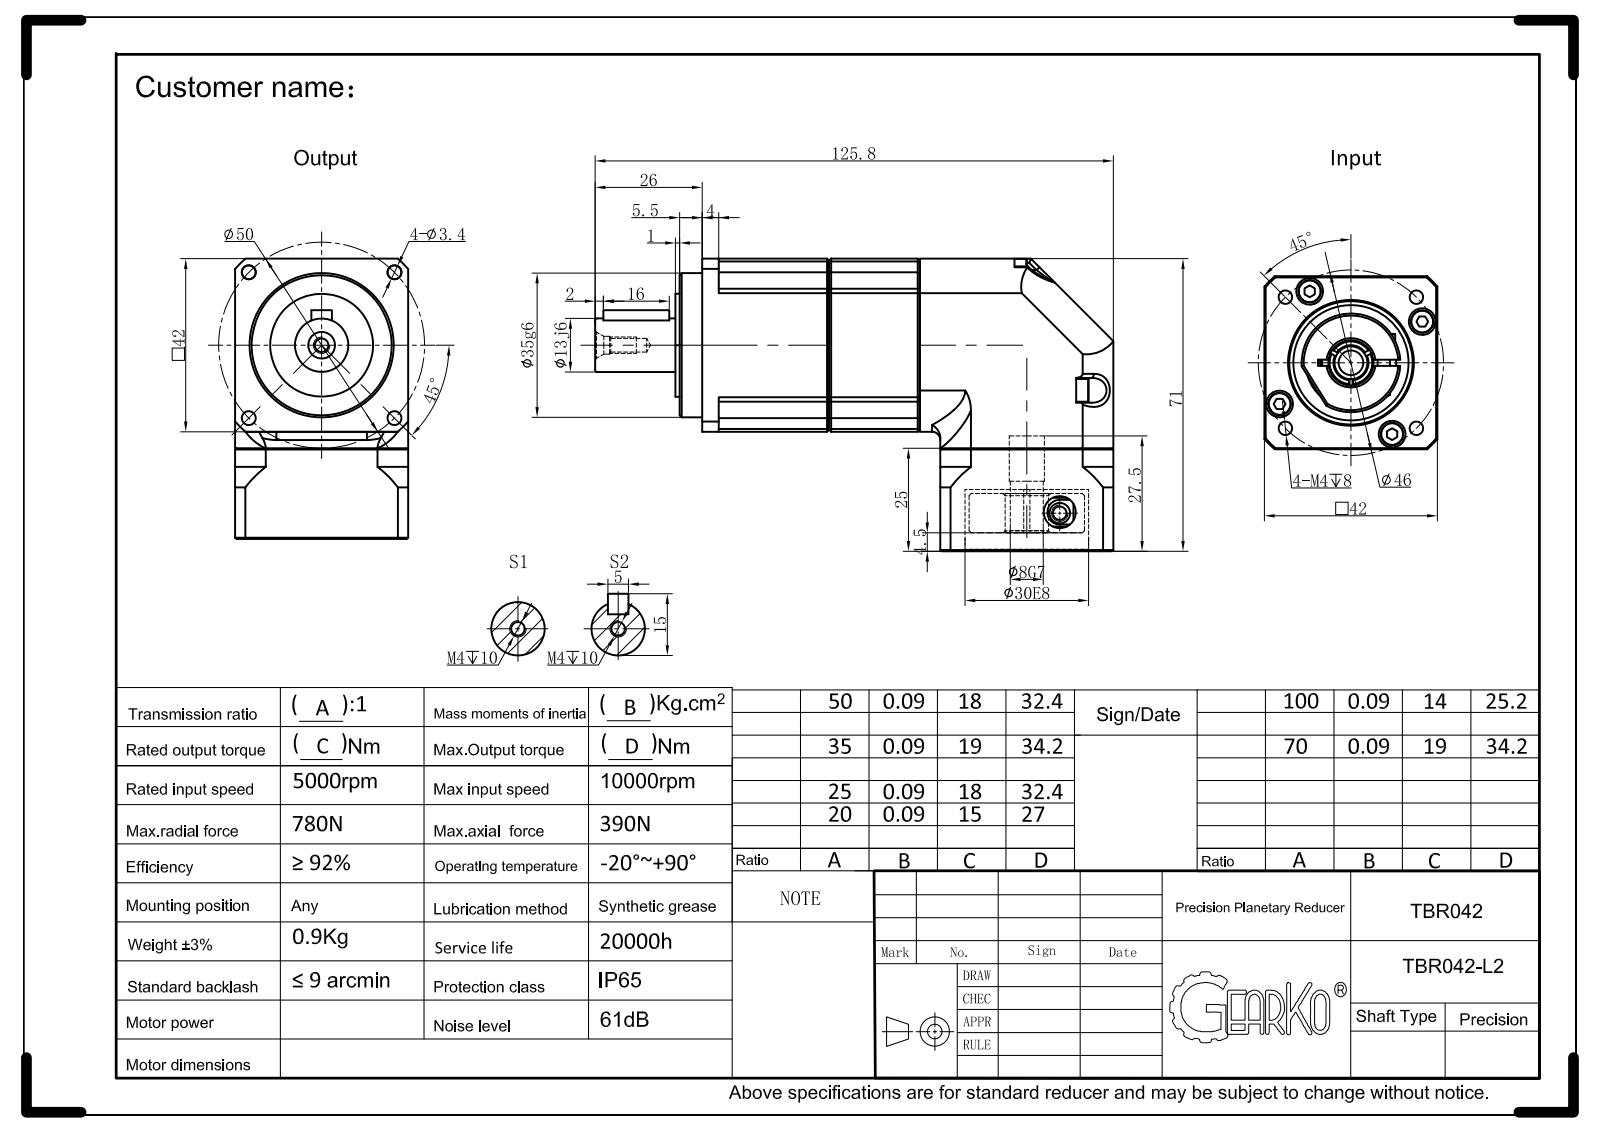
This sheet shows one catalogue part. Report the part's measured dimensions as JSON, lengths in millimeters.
{"part_name": "GB／T70．1-2000内六角圆柱头螺钉M3×30; GB／T70．1-2000内六角圆柱头螺钉M3×20; TBR042.5; TR042-L2-8-30-45-M3-28-4.5 (+5 more)", "step_written_by": "SolidWorks 2017 (CONFIG_CONTROL_DESIGN)", "units": "millimeters", "bodies": {"solids": 15, "faces": 638, "planar": 233, "cylindrical": 244, "other": 161}, "overall_size": [125.8, 70, 42.31], "volume_mm3": 164301, "surface_area_mm2": 55926, "round_holes": [[2.5, 13], [3.4, 8], [3.5, 4], [4, 4], [6.5, 4], [6.8, 2], [9, 2], [22, 2], [30, 2], [32, 2], [3.2, 1], [3.3, 1]], "round_bosses_or_shafts": [[5.5, 8], [3, 8], [37, 1], [35.6, 1], [35, 1], [25, 1], [24, 1], [23.61, 1]], "partial_cylinders_radius": [[4, 8], [1, 6], [3, 5], [10, 2], [28, 2], [2, 1], [24.5, 1], [25, 1]], "face_to_face_distances": [42, 22, 25, 4, 47, 72, 3, 46, 30, 27], "hole_center_spacings": [6.76, 21.24, 28.62, 30.04, 36.52, 45.9, 6.35, 10.28]}
